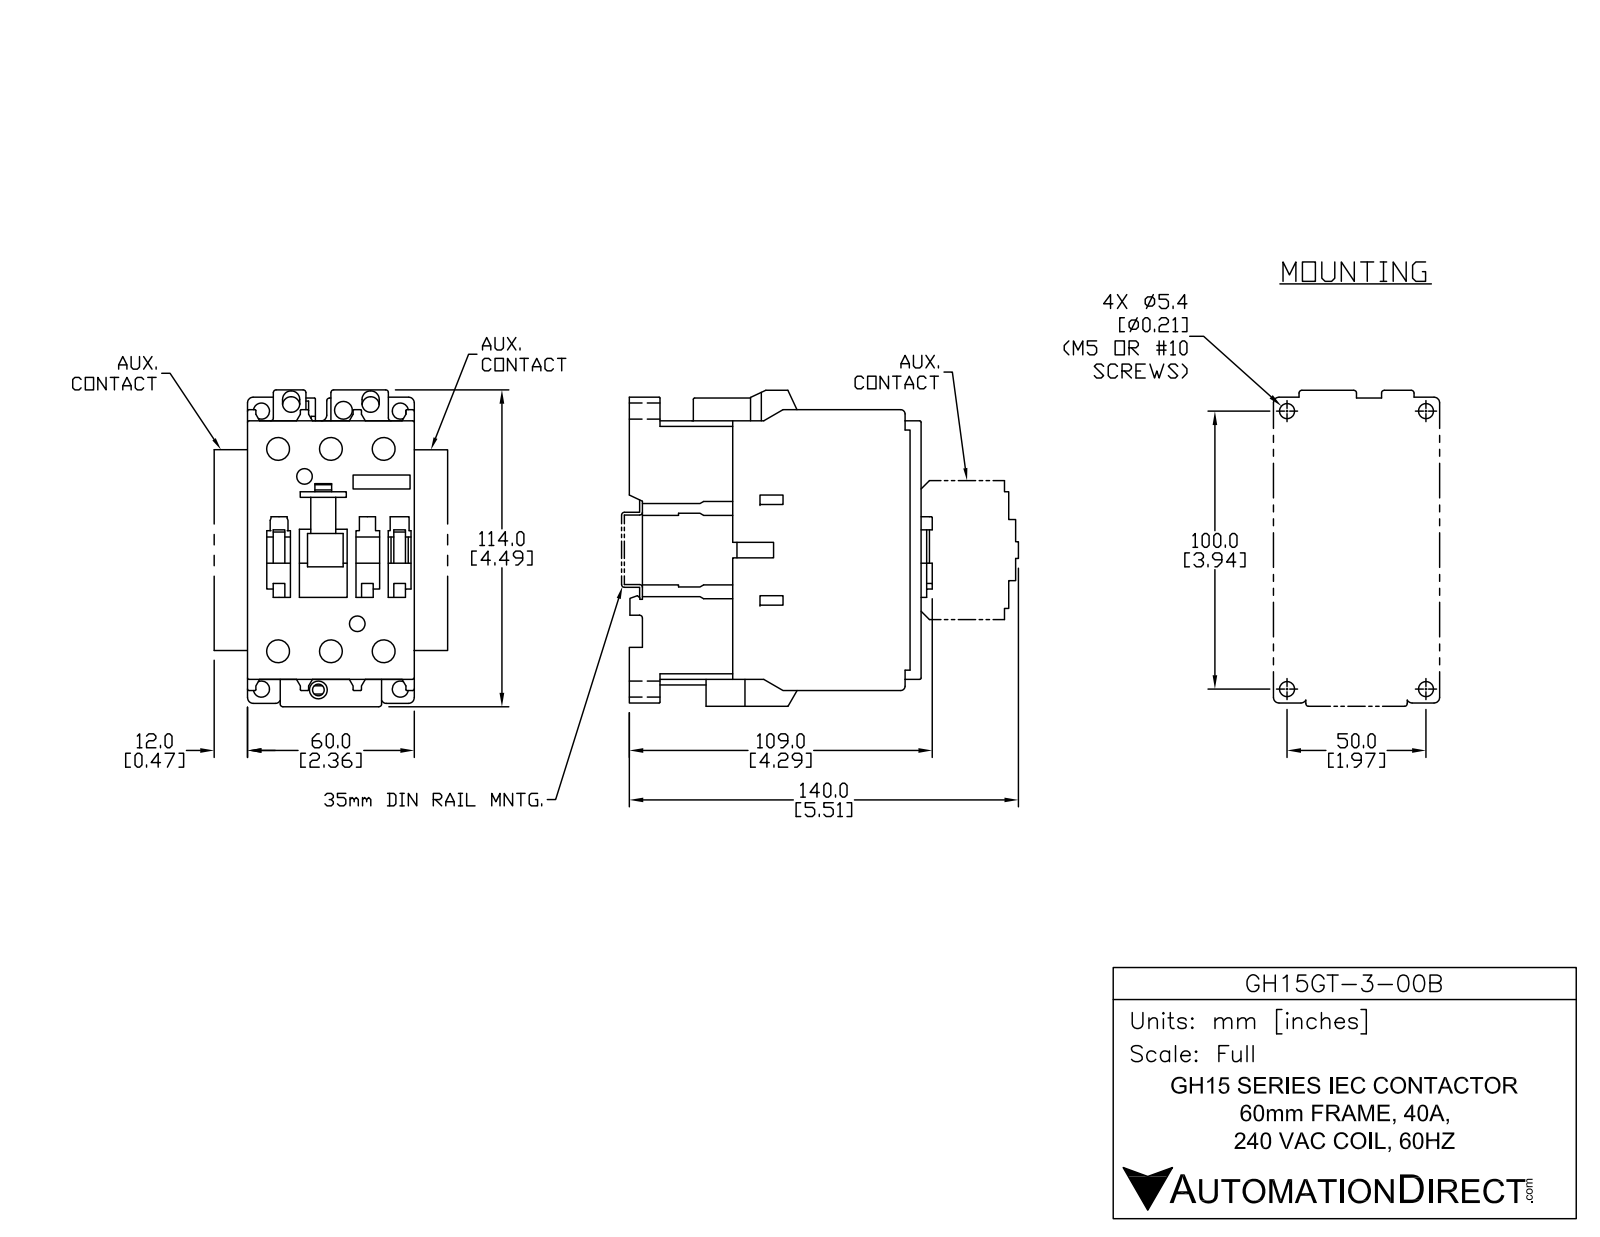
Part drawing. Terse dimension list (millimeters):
name: GH15GT-3-00B
written by: SolidWorks 2009 (AUTOMOTIVE_DESIGN)
unit: mm
bodies: 1 solid, 843 faces (634 planar, 40 cylindrical, 169 other)
size: 114 × 109.75 × 60
volume: 561 052 mm³; area: 67 816 mm²
holes: 6× ⌀8.5, 4× ⌀6, 1× ⌀5, 1× ⌀6.14, 1× ⌀6.5
rounds: 10× R2, 2× R1.23, 2× R1.25
face distances: 60, 19, 99.5, 93, 10.5, 38, 8.5, 5, 20.5, 67.25
hole spacings: 89.8, 15, 19, 28.53, 46.1, 74.95, 86.46, 96.82
